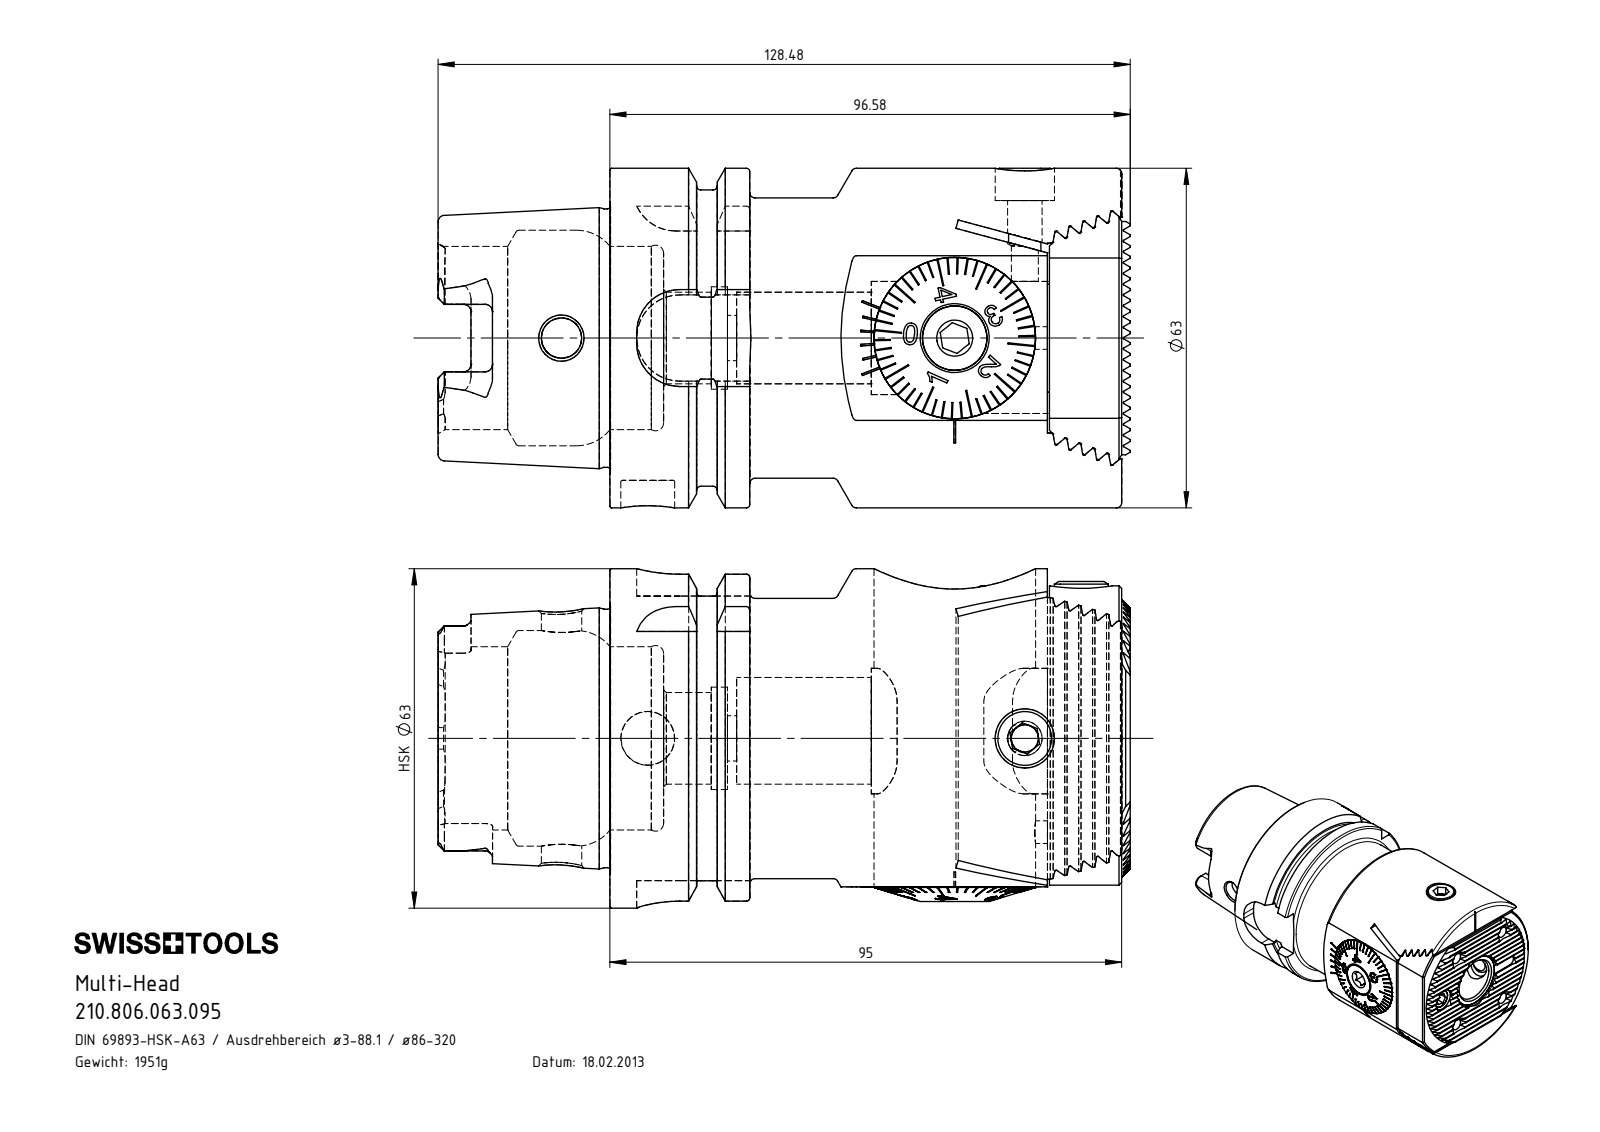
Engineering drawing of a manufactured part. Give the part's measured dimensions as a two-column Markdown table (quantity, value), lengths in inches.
| quantity | value |
| --- | --- |
| part name | A55-BG1.012.007_B; 210.806.063.095; MH1-BG1.001.049_B; A55-BG2.015.007_A (+8 more) |
| STEP written by | SolidWorks 2017 (CONFIG_CONTROL_DESIGN) |
| units | inches |
| bodies | 15 solids, 1176 faces (570 planar, 265 cylindrical, 341 other) |
| overall size | 5.058 × 2.48 × 2.48 |
| volume | 15.17 in³ |
| surface area | 117.7 in² |
| round holes (diameter × count) | 0.165 × 5, 0.335 × 4, 0.268 × 3, 0.433 × 3, 0.787 × 2, 0.039 × 1, 0.063 × 1, 0.13 × 1, 0.197 × 1, 0.252 × 1, 0.295 × 1, 0.315 × 1 |
| round bosses / shafts (diameter × count) | 0.394 × 3, 2.48 × 1, 2.163 × 1, 2.047 × 1, 1.887 × 1, 1.181 × 1, 1.18 × 1, 1.177 × 1 |
| partial cylindrical surfaces (radius × count) | 0.006 × 21, 0.008 × 20, 0.055 × 6, 0.236 × 6, 0.113 × 4, 0.315 × 4, 0.157 × 2, 1.22 × 2 |
| main face-to-face distances | 0.094, 0.016, 0.187, 0.068, 3.197, 3.213, 0.341, 0.205, 0.528, 3.74 |
| hole center spacings | 0.659, 0.71, 0.808, 0.945, 1.181, 1.37, 1.513, 0.287 |
